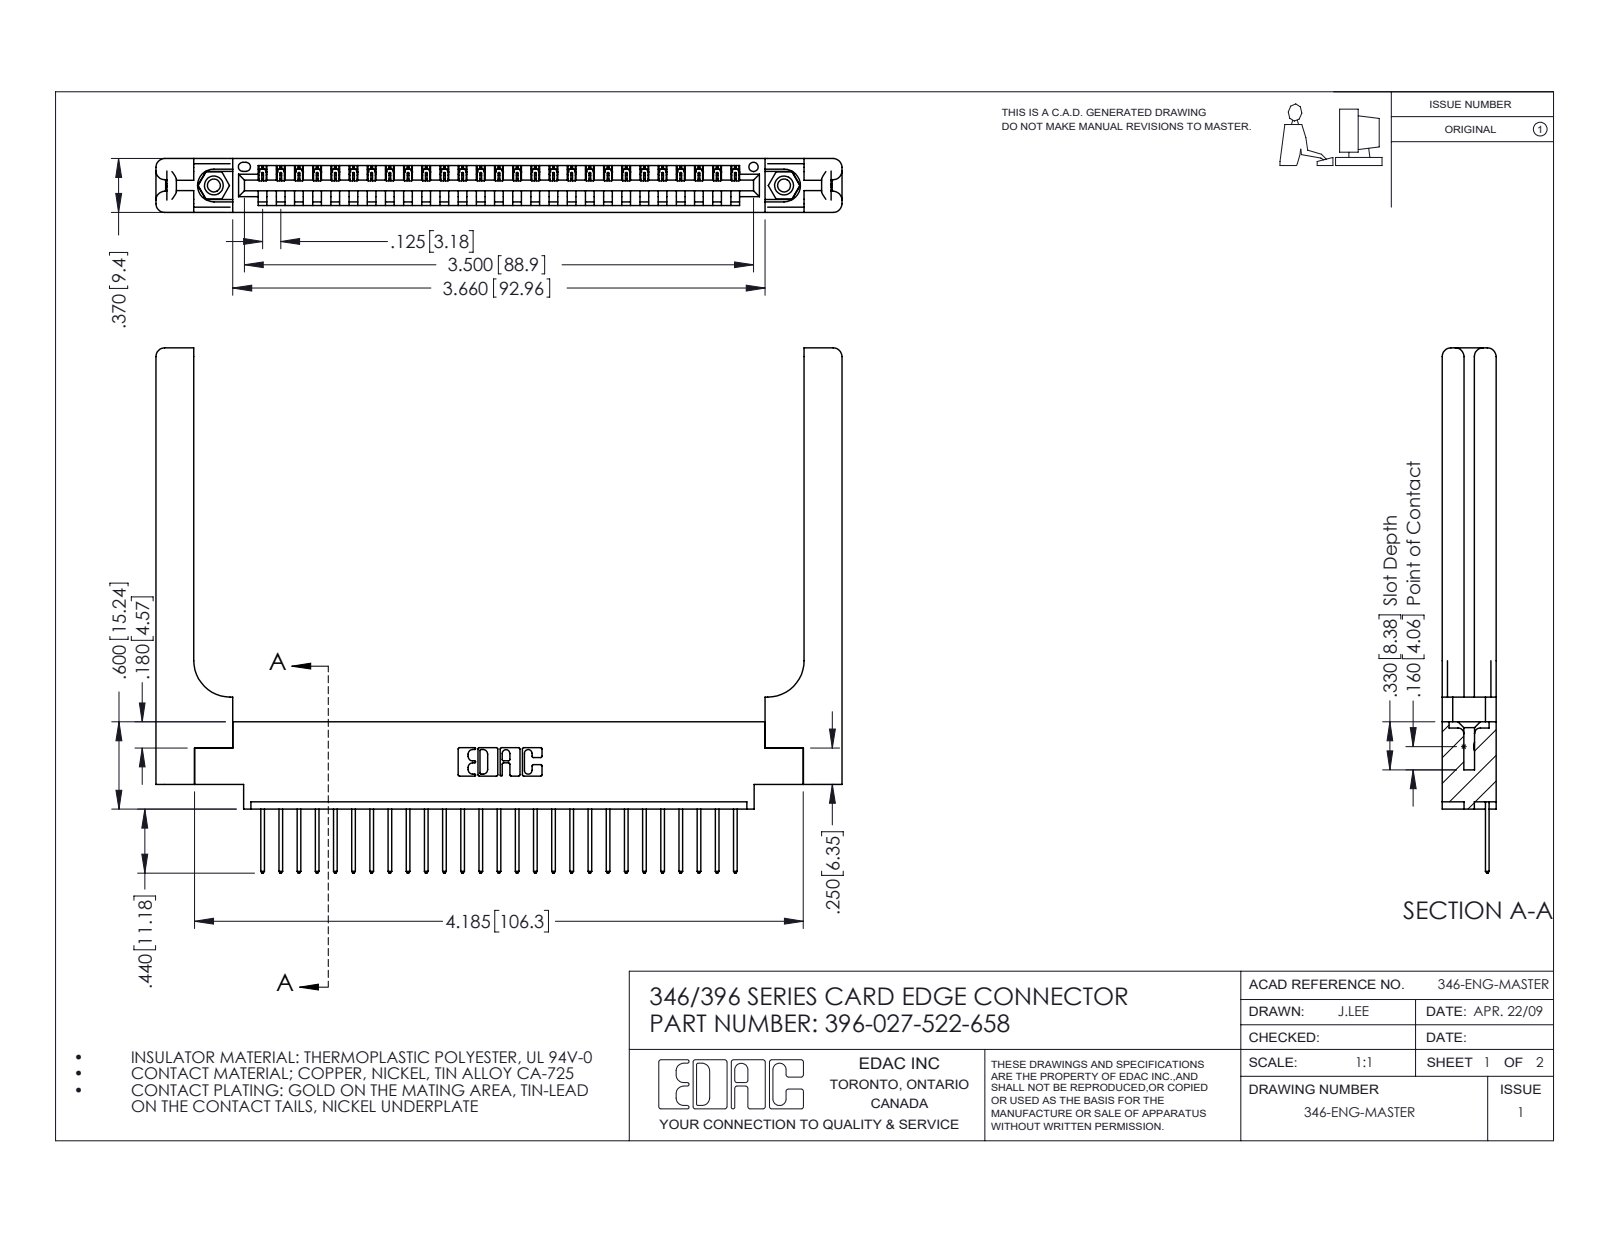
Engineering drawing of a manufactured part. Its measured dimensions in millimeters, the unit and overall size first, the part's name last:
Units: millimetres
Overall size (bounding box): 119.8 × 91.7 × 9.4
Round holes (diameter × count): ⌀2.3 ×2, ⌀3.2 ×2, ⌀4 ×2, ⌀1.6 ×1
Round bosses / shafts (diameter × count): ⌀3.9 ×2
Partial cylindrical surfaces — rounded edges, fillets, slot ends (radius × count): R0.2 ×54, R0.3 ×54, R0.3 ×22, R1.5 ×16, R0.2 ×6, R0.8 ×6, R0.7 ×3, R0.8 ×2
Main face-to-face distances: 9.4, 1.8, 1.2, 8.2, 3.8, 3.8, 6.4, 7.6, 0.6, 1.9
Hole centre spacings: 6.2, 94.3, 99.6
Volume: 18 730 mm³ · Surface area: 19 280 mm²
Bodies: 32 solids, 1948 faces (1308 planar, 580 cylindrical, 60 other)
Part name (STEP PRODUCT): 396-027-522-658; 345-250-001_345-250-001-102; 346-220-058_345-220-058; 346 Part_0.170 Offset - 0.156 Dia-TH (+1 more)
STEP written by: SolidWorks 2016 (CONFIG_CONTROL_DESIGN)
